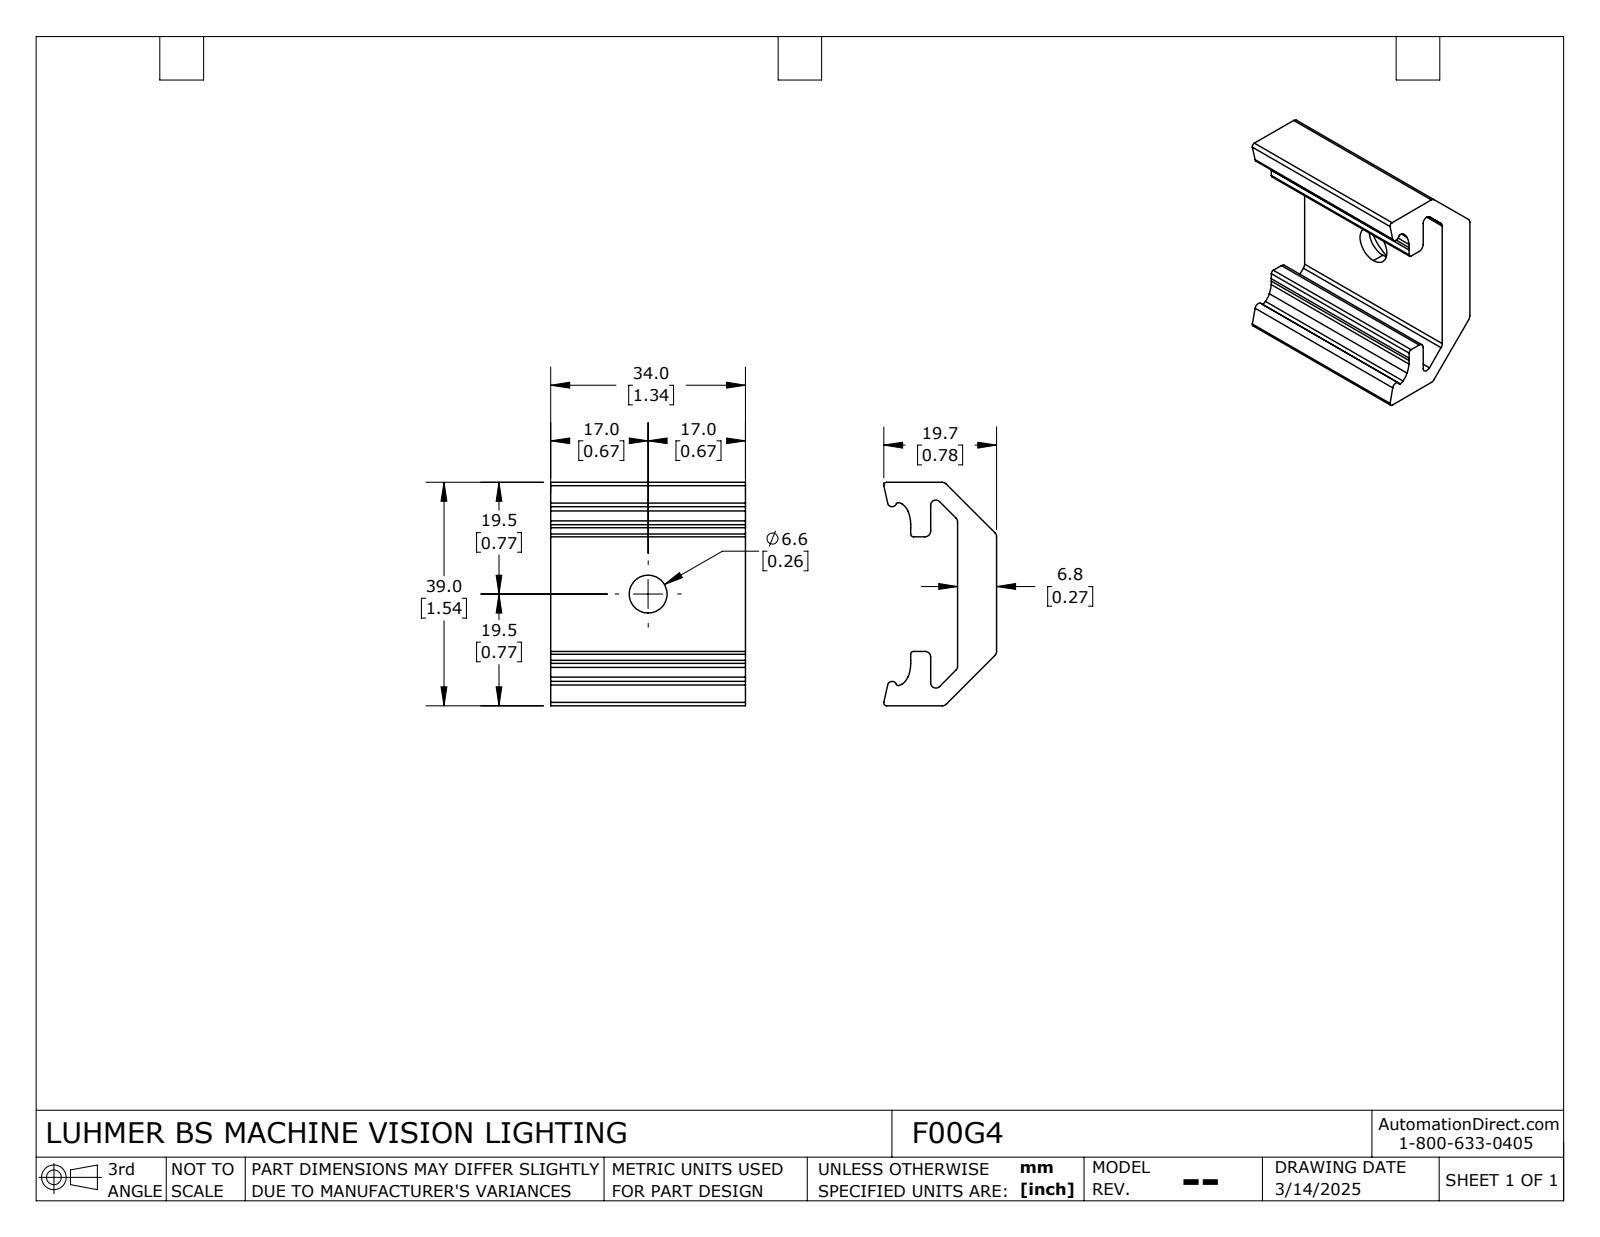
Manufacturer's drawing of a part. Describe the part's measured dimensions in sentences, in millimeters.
The part is named "F00G4". Its 3-D file was written by "SolidWorks 2024 (AUTOMOTIVE_DESIGN)". It is 1 solid with 49 faces: 19 planar, 30 cylindrical and 0 other. Overall it measures 39.01 by 34 by 19.7 millimeters. Its volume is 10 052 cubic millimeters and its surface area 5 935 square millimeters. Round holes: 1 of diameter 6.6, 1 of diameter 16.6. Partial cylindrical surfaces (rounded edges, fillets, slot ends): 8 of radius 1, 4 of radius 0.5, 2 of radius 0.3, 2 of radius 0.8, 2 of radius 0.9, 2 of radius 1.4, 2 of radius 3.1, 2 of radius 5.1. The main face-to-face distances are 6.8, 39, 34, 11.52, 4.72, 3, 4.5, 2.3, 7.02, 9.5.
